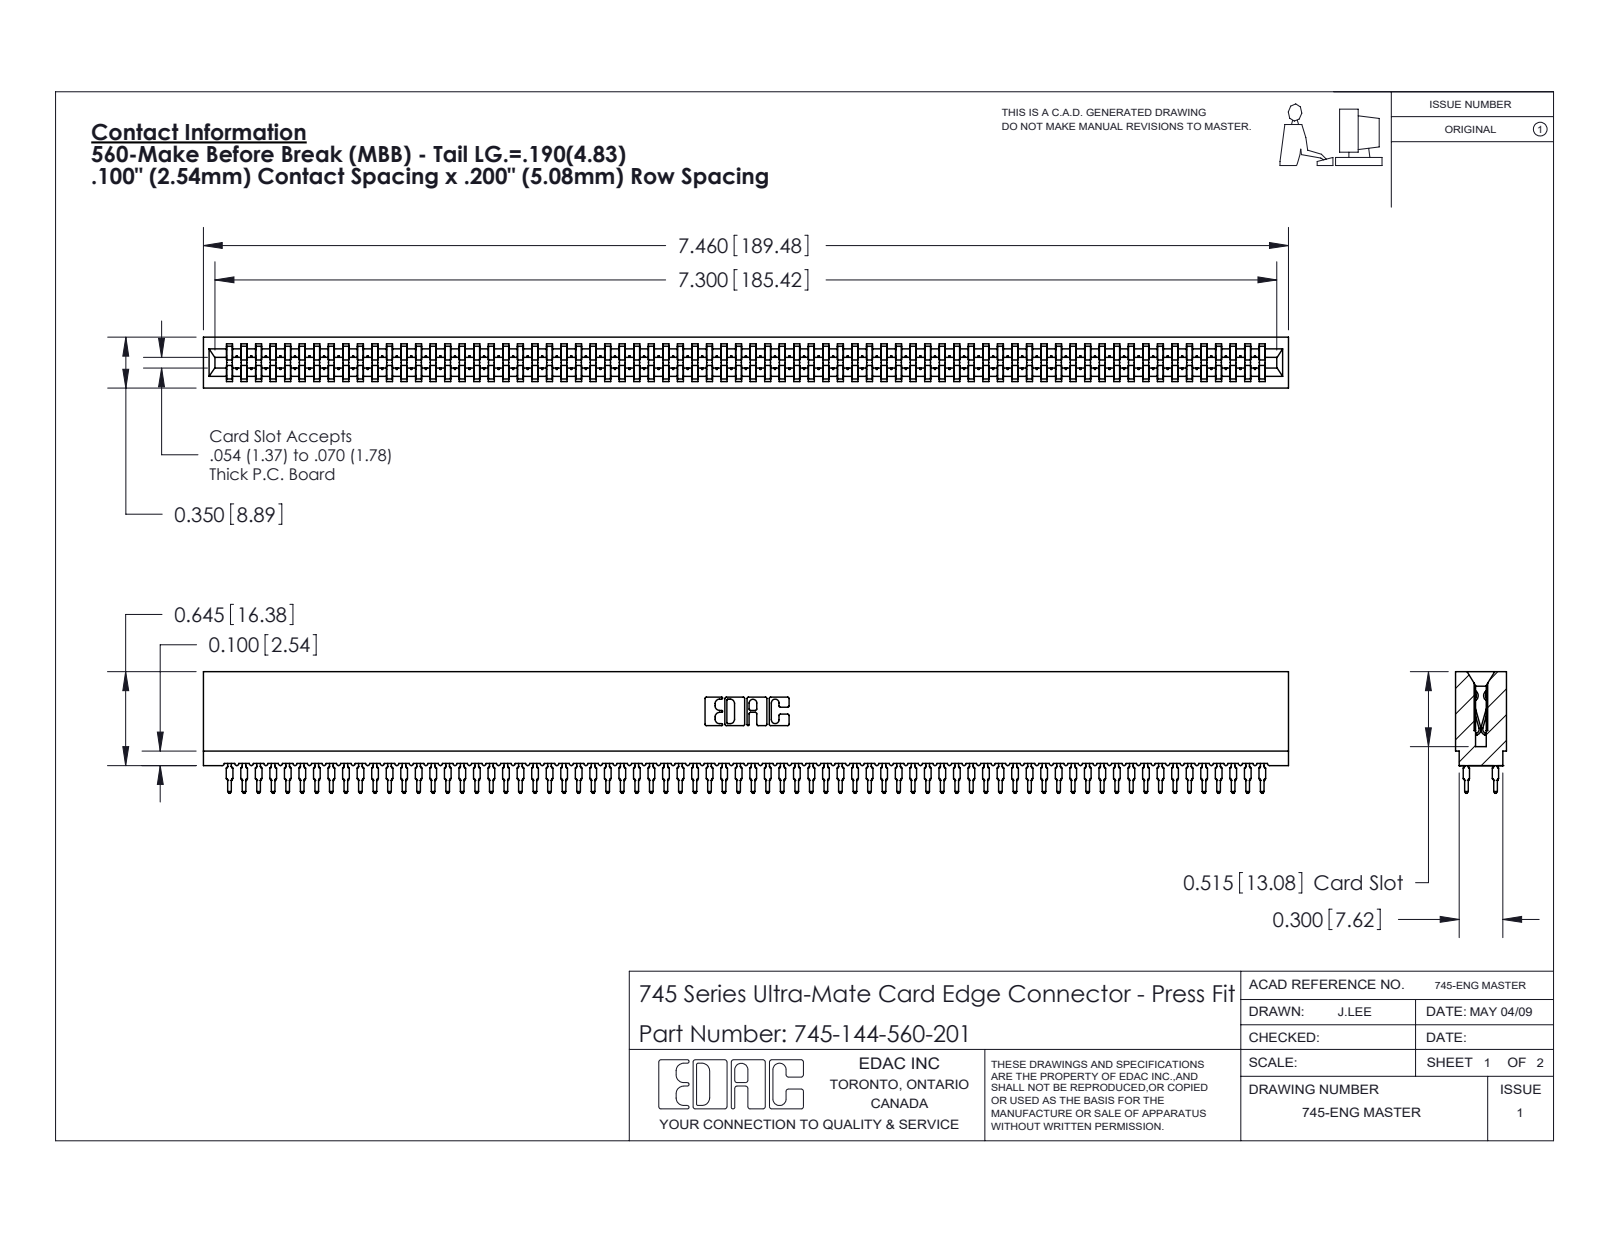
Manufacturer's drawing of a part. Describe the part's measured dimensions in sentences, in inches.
The part is named "745 Part_Insulator Option - 01; 745-292-001_560; 745-144-560-201". Its 3-D file was written by "SolidWorks 2020 (CONFIG_CONTROL_DESIGN)". It is 145 solids with 14279 faces: 7399 planar, 3136 cylindrical and 3744 other. Overall it measures 7.46 by 0.836 by 0.35 inches. Its volume is 1.063 cubic inches and its surface area 59.48 square inches. Partial cylindrical surfaces (rounded edges, fillets, slot ends): 288 of radius 0.021, 144 of radius 0.015, 22 of radius 0.01, 8 of radius 0.005, 8 of radius 0.011, 6 of radius 0.007, 6 of radius 0.031, 3 of radius 0.026. The main face-to-face distances are 0.35, 0.063, 0.287, 0.045, 0.305, 0.018, 0.243, 0.138, 0.212, 0.093.
